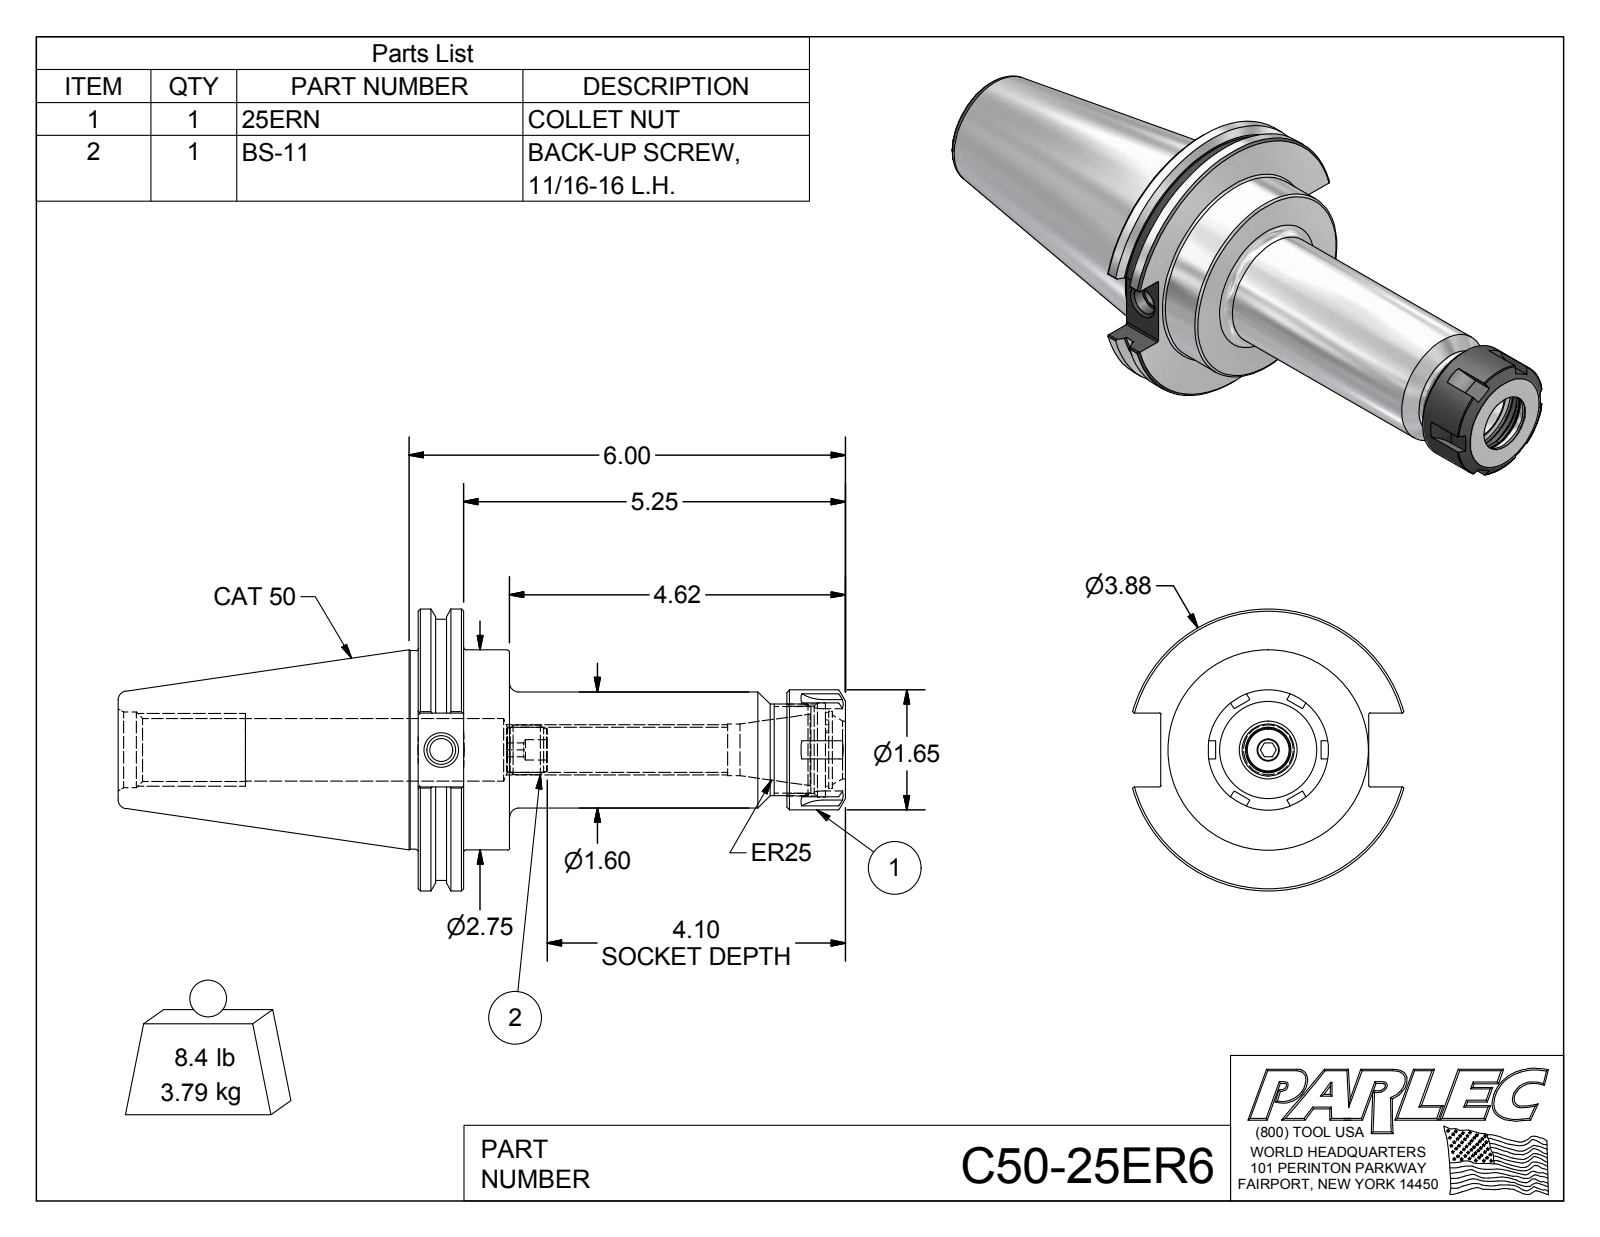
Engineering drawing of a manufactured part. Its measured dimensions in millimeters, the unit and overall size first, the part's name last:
Units: millimetres
Overall size (bounding box): 254 × 98.4 × 94.7
Round holes (diameter × count): ⌀7.1 ×1, ⌀8 ×1, ⌀10.1 ×1, ⌀15.7 ×1, ⌀18 ×1, ⌀20.2 ×1, ⌀21.9 ×1, ⌀22 ×1, ⌀26.4 ×1, ⌀26.8 ×1, ⌀30.5 ×1, ⌀32.9 ×1
Round bosses / shafts (diameter × count): ⌀98.4 ×1, ⌀91.3 ×1, ⌀69.9 ×1, ⌀69.3 ×1, ⌀42 ×1, ⌀40.5 ×1, ⌀32 ×1, ⌀17.3 ×1
Partial cylindrical surfaces — rounded edges, fillets, slot ends (radius × count): R0.5 ×8, R12.7 ×6, R12 ×1, R13.1 ×1
Main face-to-face distances: 15.9, 31.9, 16, 149.2, 133.4, 117.3, 128.7, 112.9, 96.9, 20.5
Volume: 491 900 mm³ · Surface area: 74 650 mm²
Bodies: 3 solids, 153 faces (65 planar, 45 cylindrical, 43 other)
Part name (STEP PRODUCT): C50-25ER6; C50-25ER6-1; 25ERN; BS-11
STEP written by: Autodesk Inventor 2012 (AUTOMOTIVE_DESIGN)
